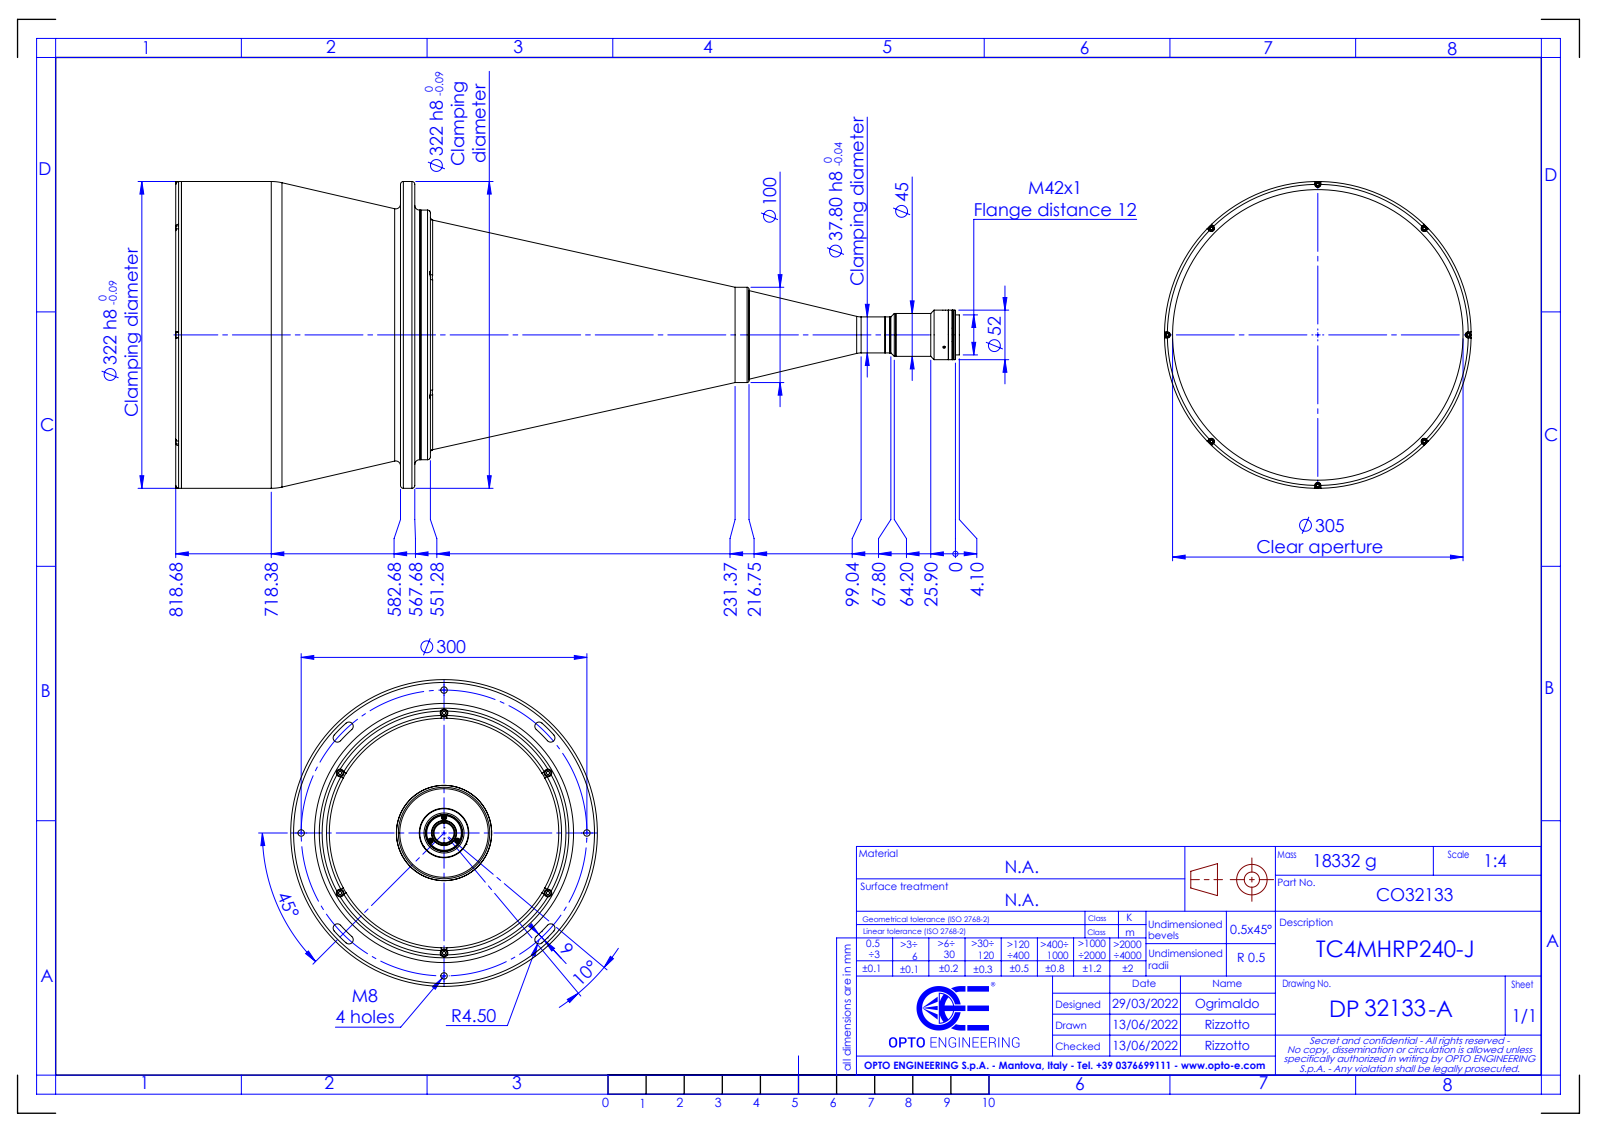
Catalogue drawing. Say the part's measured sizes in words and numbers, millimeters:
The part is named "DP32133-A_TC4MHRP240-J". Its 3-D file was written by "SolidWorks 2021 (CONFIG_CONTROL_DESIGN)". It is 0 solids with 252 faces: 69 planar, 106 cylindrical and 77 other. Overall it measures 822.77 by 322 by 322 millimeters. Round holes: 6 of diameter 8, 4 of diameter 6.8, 2 of diameter 2.5, 1 of diameter 38, 1 of diameter 305, 1 of diameter 310, 1 of diameter 316. Round bosses or shafts: 8 of diameter 5.5, 1 of diameter 322, 1 of diameter 262, 1 of diameter 100, 1 of diameter 52, 1 of diameter 51.8, 1 of diameter 45, 1 of diameter 42. Partial cylindrical surfaces (rounded edges, fillets, slot ends): 8 of radius 4.5, 1 of radius 145.5, 1 of radius 154.5. The main face-to-face distances are 15, 230, 245, 251.4, 21.4, 6.4, 6, 236, 251, 257.4. The hole center spacings are 126, 218.24, 75.1, 139.56, 150, 195.9, 212.13, 239.32.
